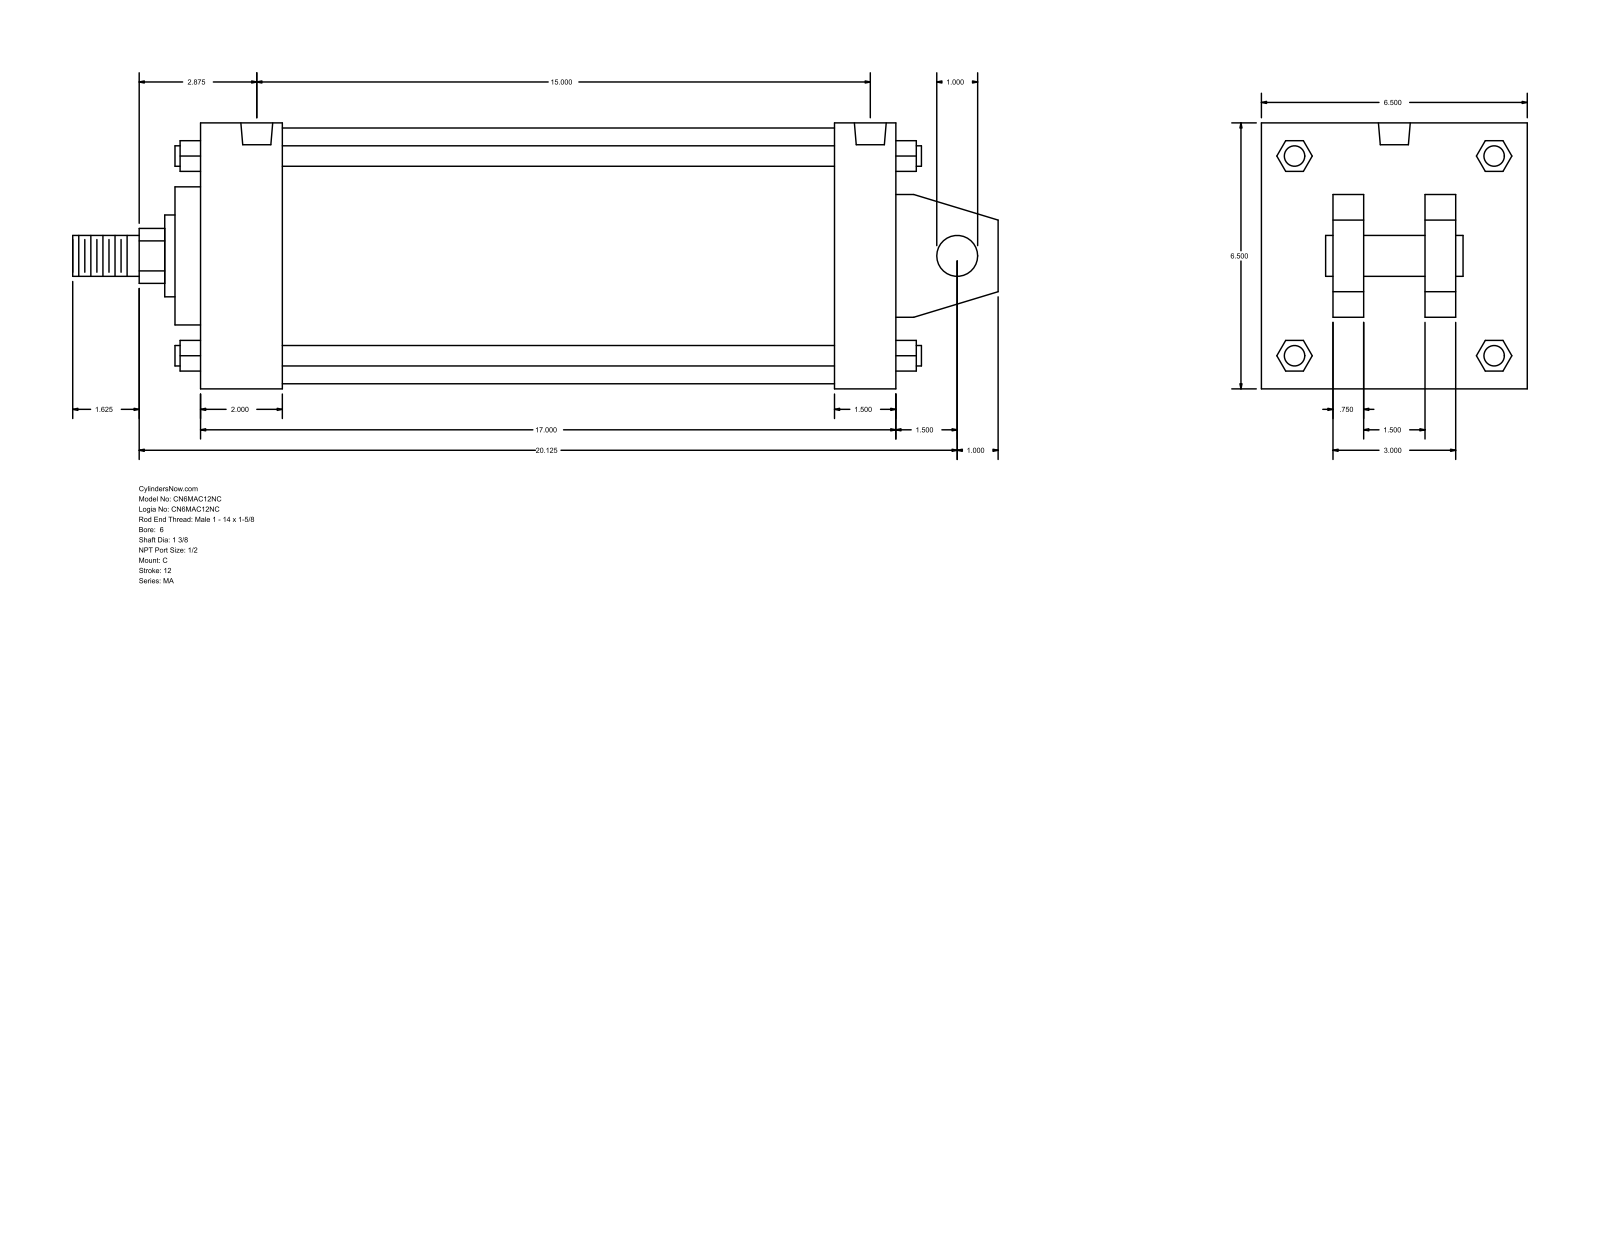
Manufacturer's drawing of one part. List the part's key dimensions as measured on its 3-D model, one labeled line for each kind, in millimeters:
Part name (STEP PRODUCT): MA_C__0600_1.375
STEP written by: GSSL Pune (CONFIG_CONTROL_DESIGN)
Units: millimetres
Bodies: 0 solids, 141 faces (109 planar, 32 cylindrical, 0 other)
Overall size (bounding box): 574.67 × 165.1 × 165.1
Round holes (diameter × count): ⌀17.46 ×4, ⌀19.77 ×2
Round bosses / shafts (diameter × count): ⌀12.7 ×4, ⌀25.4 ×2, ⌀158.75 ×1, ⌀85.72 ×1, ⌀50.8 ×1, ⌀34.92 ×1
Partial cylindrical surfaces — rounded edges, fillets, slot ends (radius × count): R17.06 ×1
Main face-to-face distances: 165.1, 431.8, 38.1, 19.05, 63.5, 101.6, 50.8, 44.45, 120.65, 393.7
Hole centre spacings: 381, 3.17, 3.18, 377.82, 380.99, 384.17
